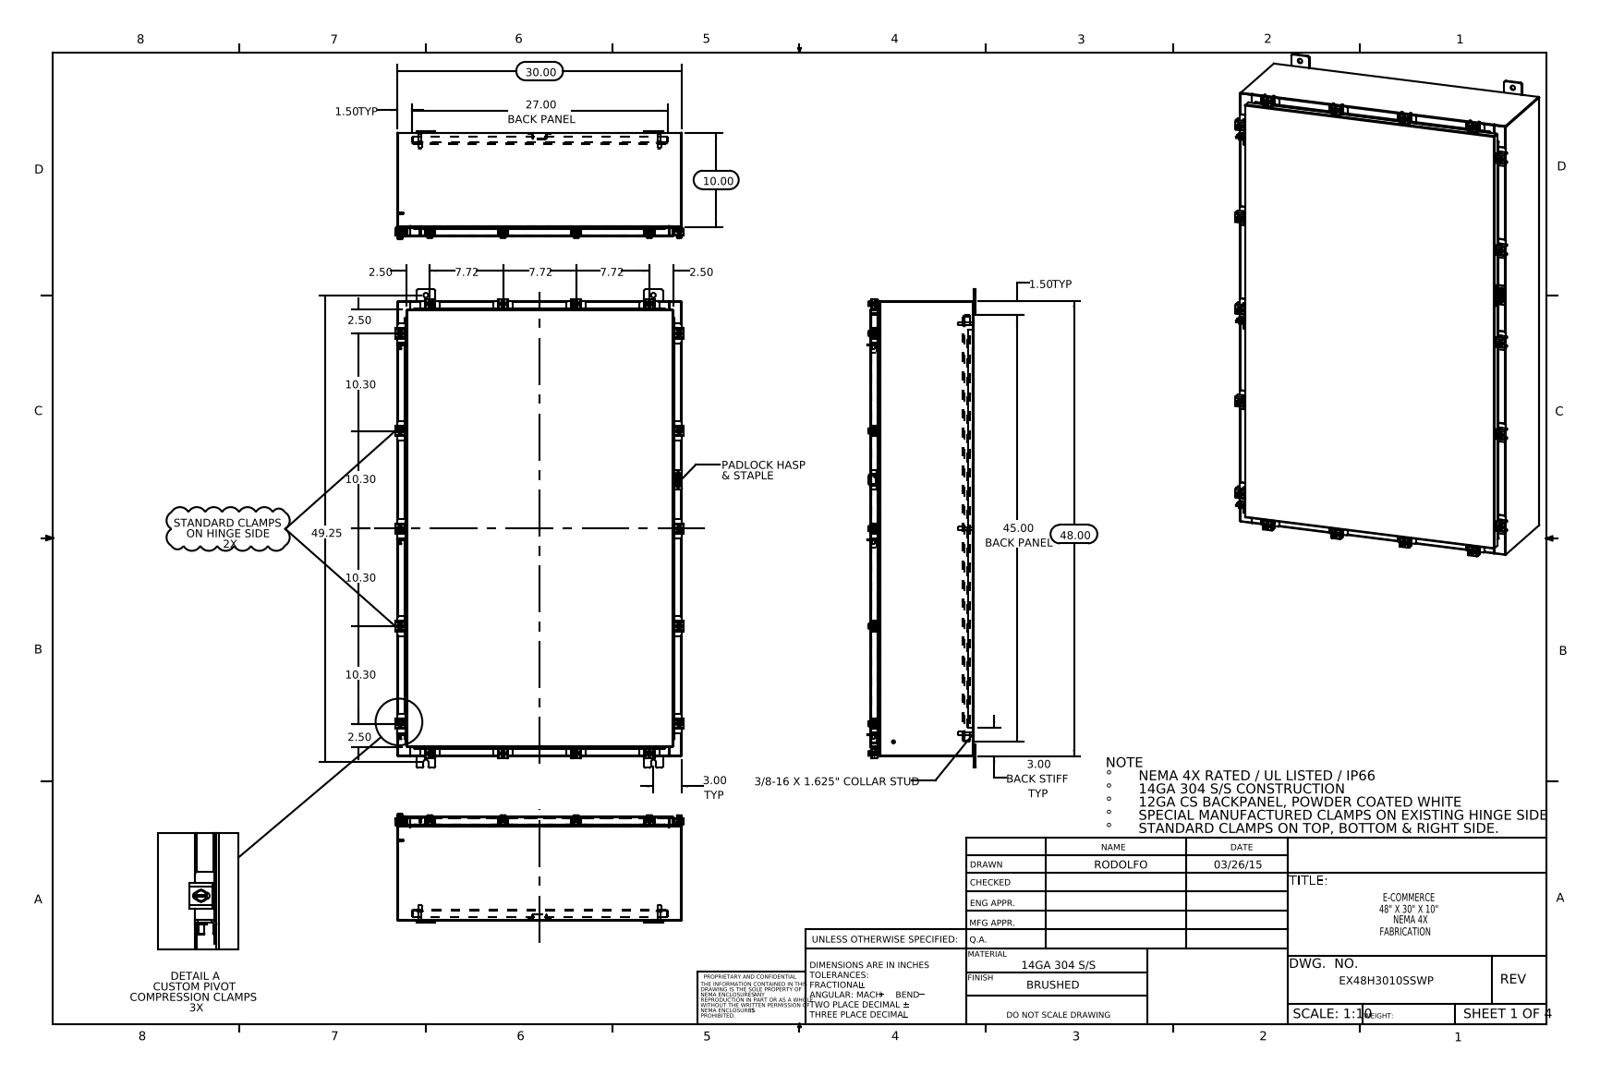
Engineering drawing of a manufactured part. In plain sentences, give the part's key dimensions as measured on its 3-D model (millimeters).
The part is named "EX48H3010SSWP Cover; EX48H3010SSWP Special Clamp; N-WMT04X30402202210-00 22104005_DEFAULT; EX48H3010SSWP Clamp Bracket (+8 more)". Its 3-D file was written by "SolidWorks 2014 (CONFIG_CONTROL_DESIGN)". It is 116 solids with 2878 faces: 1525 planar, 1123 cylindrical and 230 other. Overall it measures 1282.7 by 772.7 by 290.9 millimeters. Its volume is 8 462 000 cubic millimeters and its surface area 8 257 000 square millimeters. Round holes: 18 of diameter 5.4, 18 of diameter 6.6, 10 of diameter 12.7, 1 of diameter 3.2, 1 of diameter 6.4. Round bosses or shafts: 18 of diameter 12.7, 18 of diameter 6.4, 15 of diameter 10.1, 6 of diameter 15.9, 6 of diameter 9.5, 6 of diameter 8.4, 2 of diameter 8, 2 of diameter 6. Partial cylindrical surfaces (rounded edges, fillets, slot ends): 76 of radius 1.5, 36 of radius 3.6, 33 of radius 3, 30 of radius 0.3, 27 of radius 2.3, 26 of radius 2.2, 25 of radius 1.3, 24 of radius 3.7. The main face-to-face distances are 1.9, 276.9, 275, 278.8, 2.6, 25.4, 27.3, 249.6, 251.5, 29.9. The hole center spacings are 792.5, 748.1, 59.6, 112.8, 261.6, 525.8, 549.3, 603.2.
